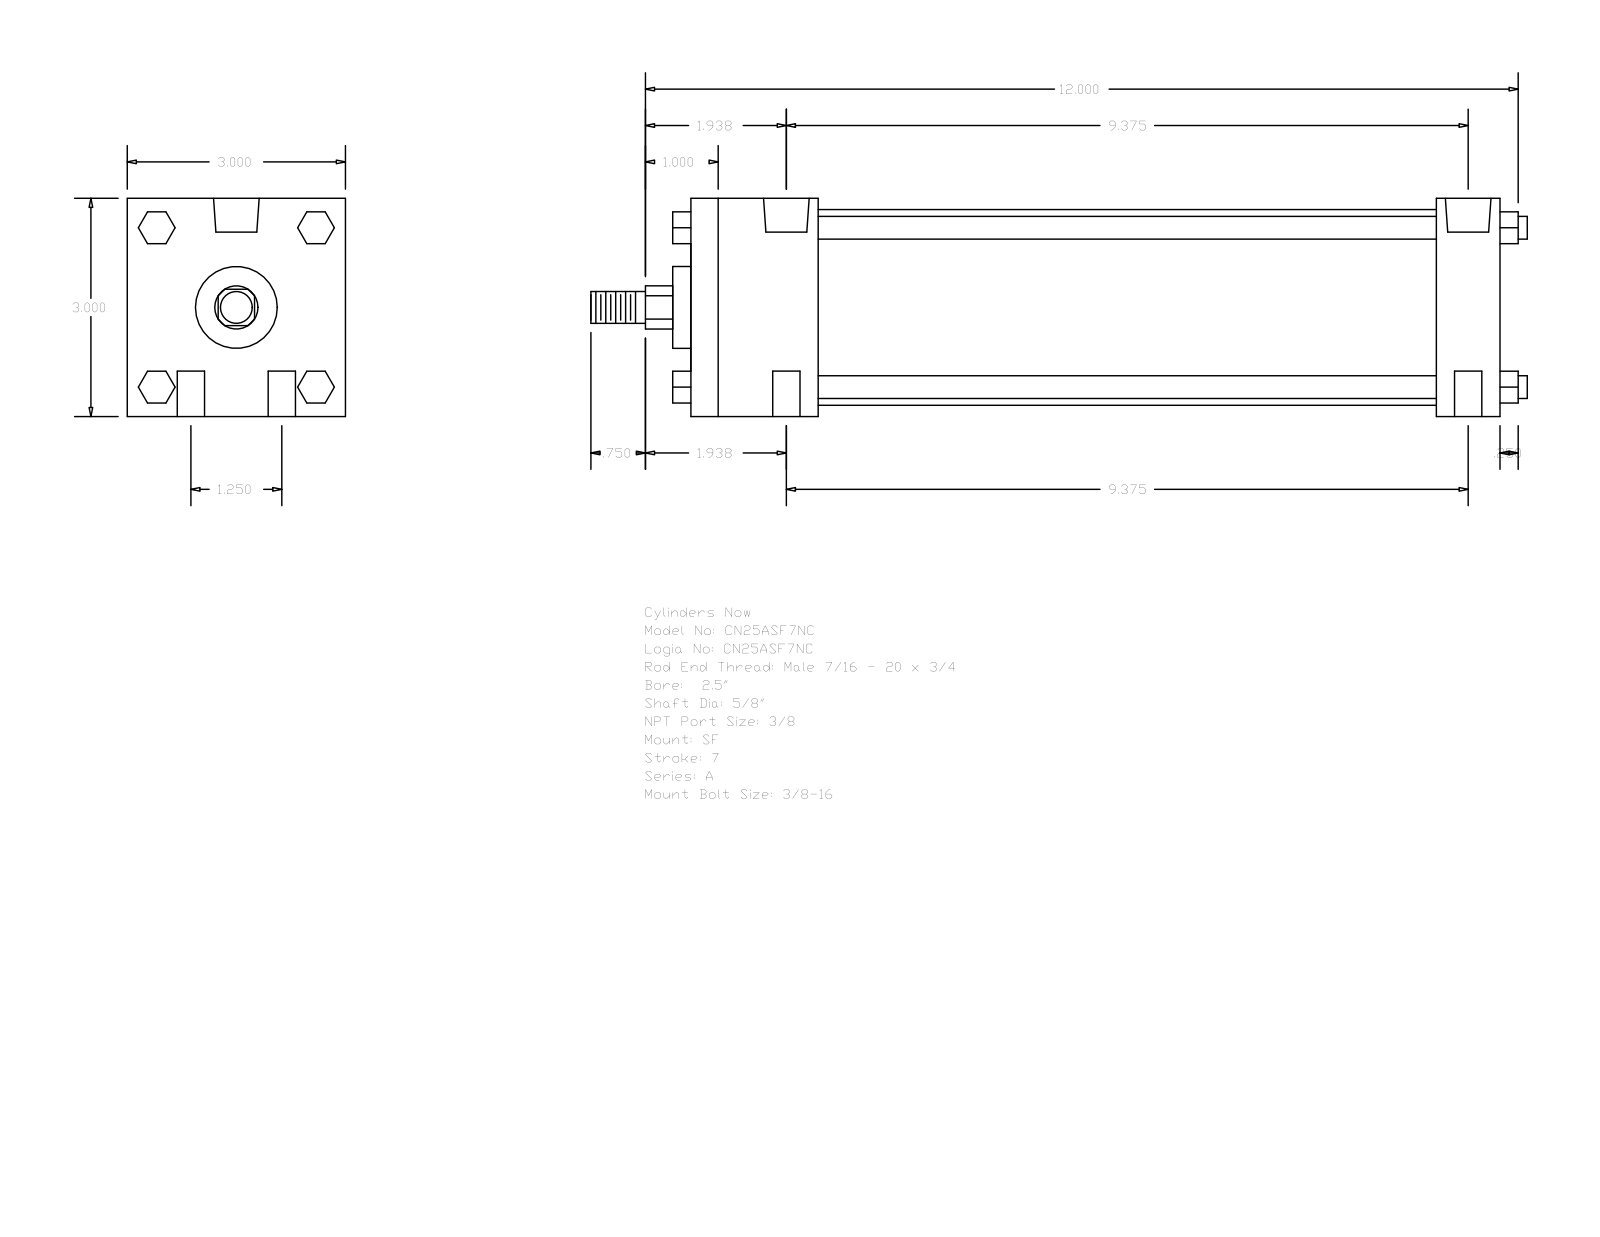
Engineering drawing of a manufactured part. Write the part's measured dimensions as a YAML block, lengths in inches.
part_name: "A_SF__0250_0.625"
step_written_by: "GSSL Pune (CONFIG_CONTROL_DESIGN)"
units: inches
bodies: {solids: 0, faces: 124, planar: 94, cylindrical: 30, other: 0}
overall_size: [12.875, 3, 3]
round_holes:
  - {diameter: 0.375, count: 4}
  - {diameter: 0.219, count: 2}
  - {diameter: 0.627, count: 2}
round_bosses_or_shafts:
  - {diameter: 0.313, count: 4}
  - {diameter: 2.69, count: 1}
  - {diameter: 1.125, count: 1}
  - {diameter: 0.625, count: 1}
  - {diameter: 0.437, count: 1}
partial_cylinders:
  - {radius: 0.297, count: 1}
face_to_face_distances: [3, 11.125, 1.75, 10.25, 0.875, 8.5, 9.375, 0.25, 11.375, 2]
hole_center_spacings: [0.625, 9.396, 9.375, 1.25, 9.458, 9.563]
